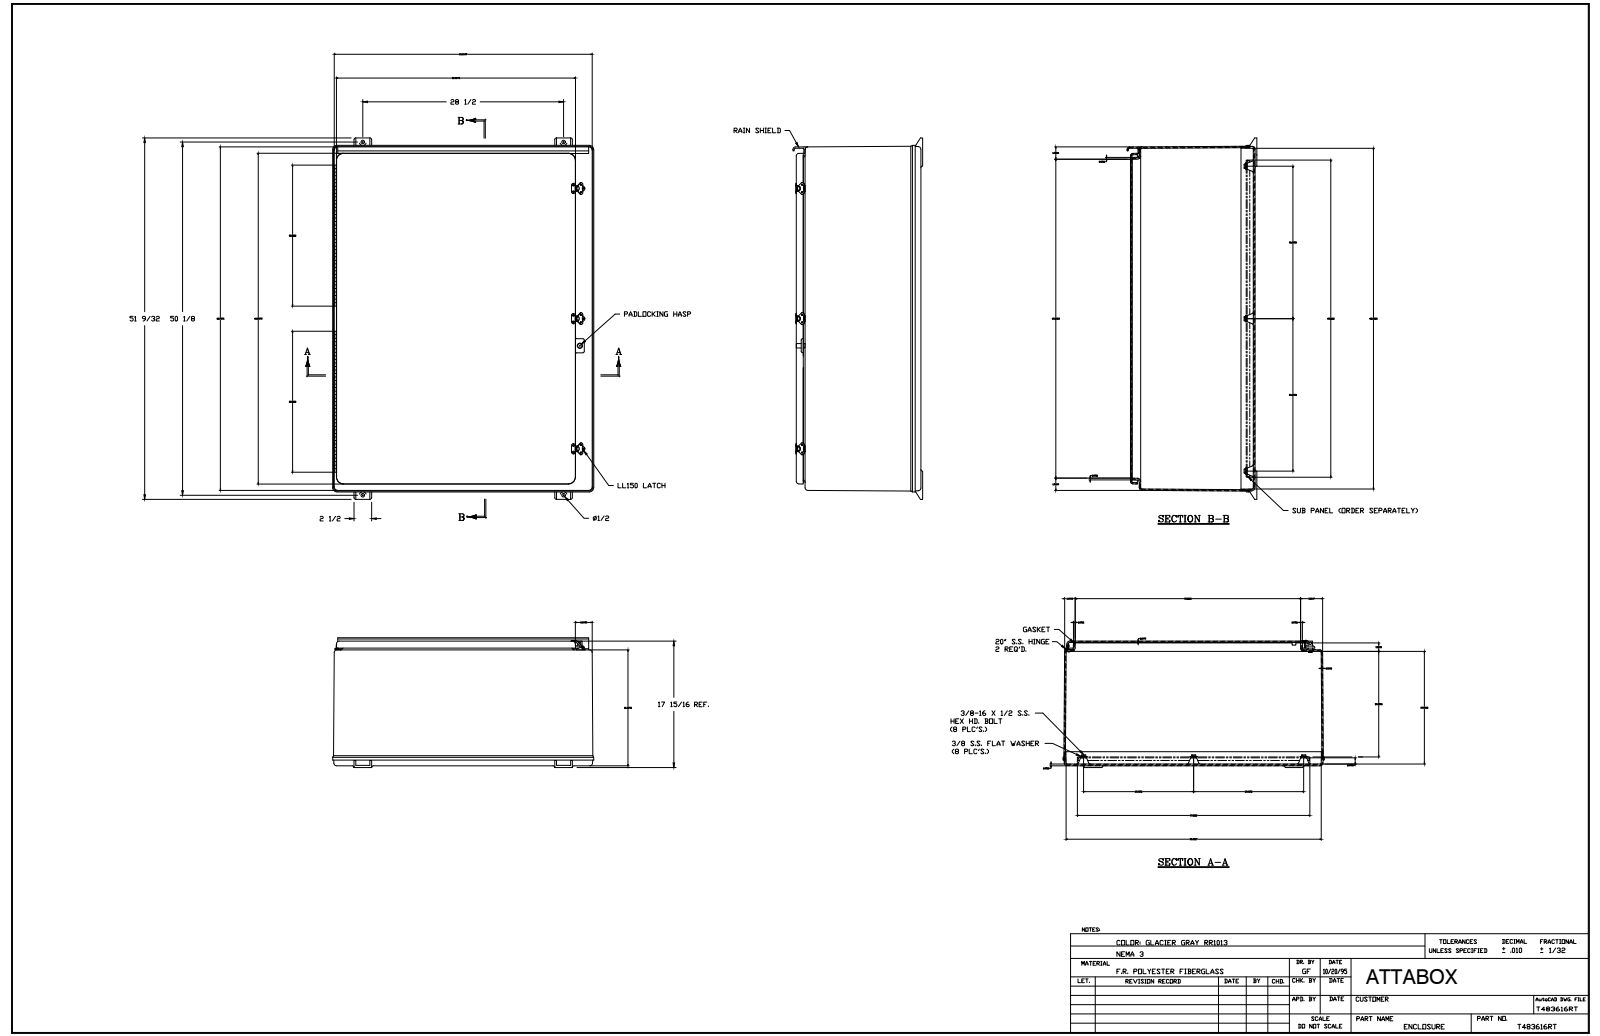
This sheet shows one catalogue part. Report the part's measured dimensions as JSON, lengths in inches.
{"part_name": "T483616RT", "step_written_by": "SolidWorks 2018 (AUTOMOTIVE_DESIGN)", "units": "inches", "bodies": {"solids": 83, "faces": 1938, "planar": 788, "cylindrical": 797, "other": 353}, "overall_size": [51.281, 37.063, 18.454], "volume_in3": 1477, "surface_area_in2": 14409, "round_holes": [[0.13, 55], [0.063, 26], [0.138, 20], [0.065, 10], [0.065, 9], [0.563, 8], [0.187, 6], [0.145, 2], [0.281, 2], [0.51, 2], [0.51, 2], [0.125, 1]], "round_bosses_or_shafts": [[0.14, 26], [0.297, 19], [0.5, 3], [0.25, 1], [0.201, 1], [0.2, 1], [0.135, 1]], "partial_cylinders_radius": [[0.01, 86], [0.25, 24], [0.21, 20], [0.375, 13], [0.03, 12], [0.187, 12], [0.312, 12], [0.5, 12]], "face_to_face_distances": [0.203, 0.25, 17.673, 17.423, 17.485, 17.235, 0.188, 16.454, 16.204, 1.031], "hole_center_spacings": [18.469, 23.563, 6.375, 6.375, 12.625, 12.625, 6.25, 19]}
